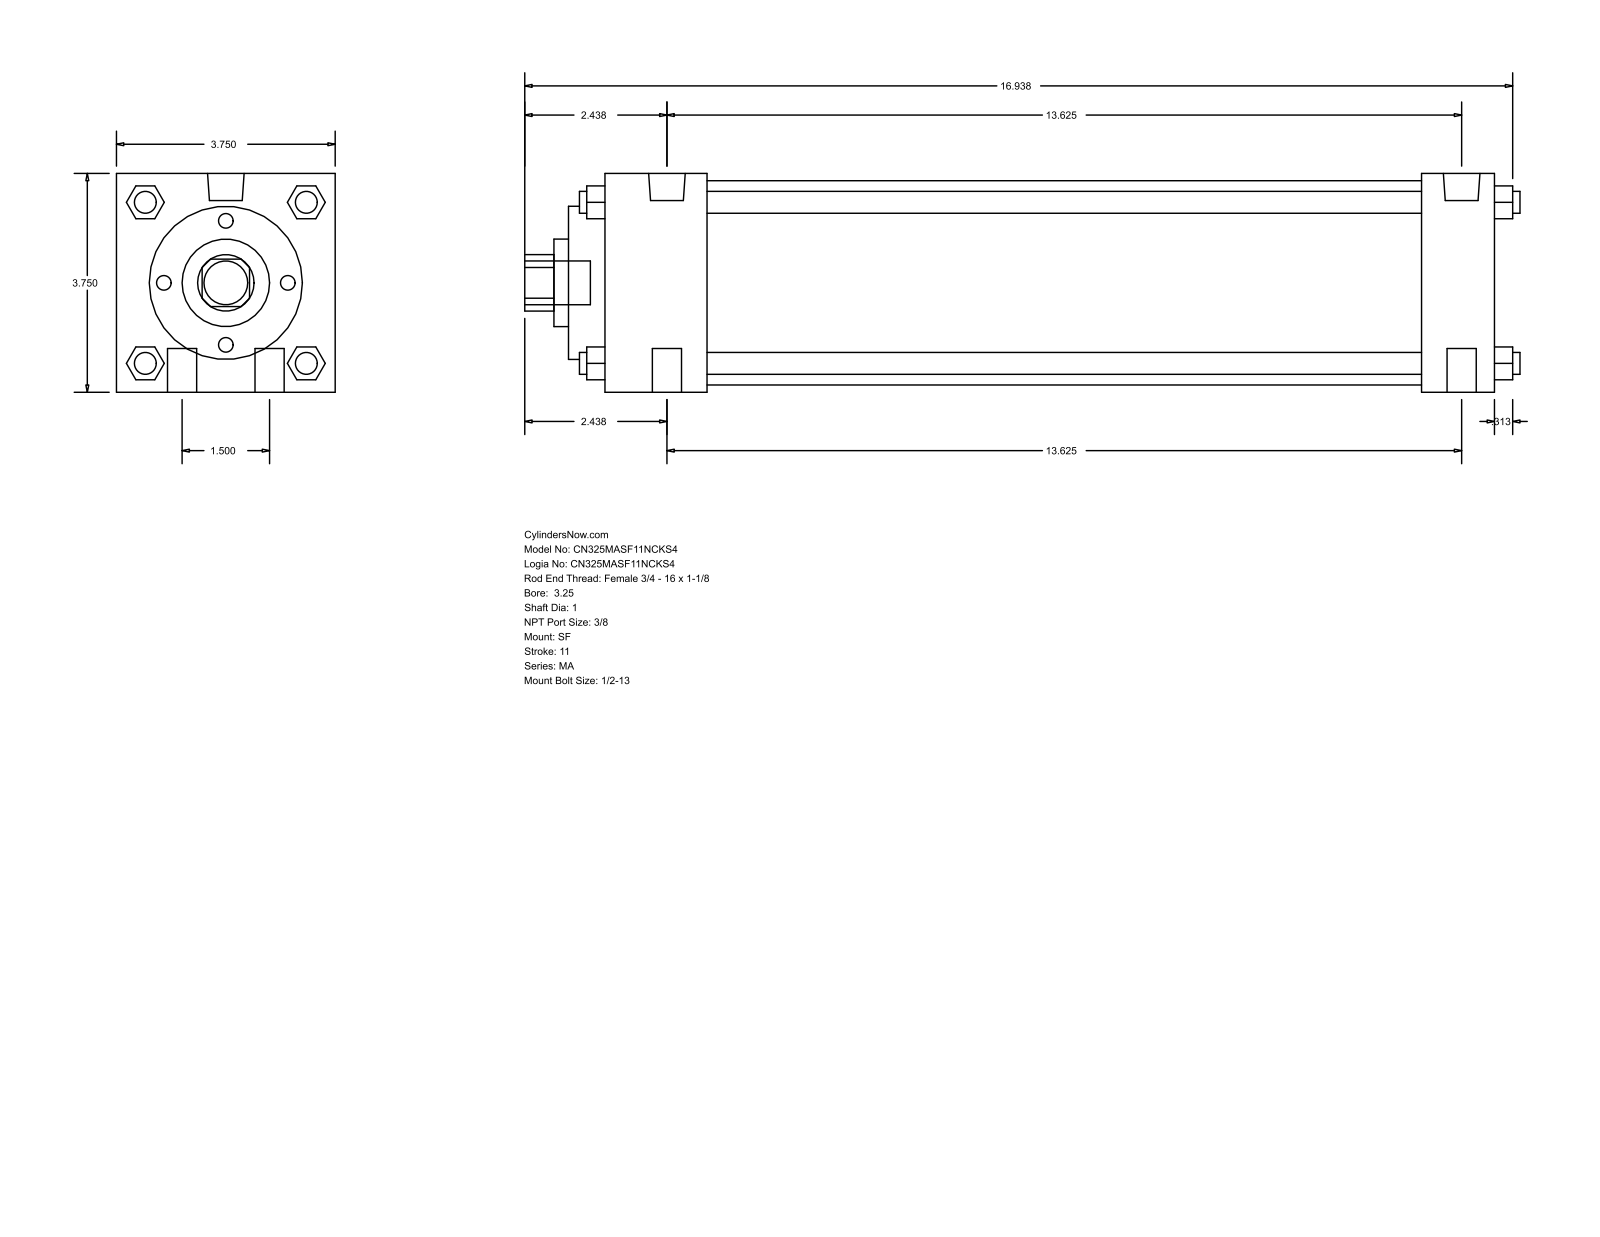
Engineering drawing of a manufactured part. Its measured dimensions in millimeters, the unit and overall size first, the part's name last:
Units: millimetres
Overall size (bounding box): 433.39 × 95.25 × 95.25
Round holes (diameter × count): ⌀25.4 ×1, ⌀38.1 ×1, ⌀66.67 ×1, ⌀88.9 ×1
Round bosses / shafts (diameter × count): ⌀12.7 ×4, ⌀9.53 ×4, ⌀15.93 ×2, ⌀11.11 ×2, ⌀19.05 ×1
Partial cylindrical surfaces — rounded edges, fillets, slot ends (radius × count): R12.29 ×1
Main face-to-face distances: 95.24, 387.35, 403.22, 15.87, 355.6, 31.75, 44.46, 311.14, 342.89, 60.33
Bodies: 0 solids, 126 faces (95 planar, 31 cylindrical, 0 other)
Part name (STEP PRODUCT): MA_SF__0325_1
STEP written by: GSSL Pune (CONFIG_CONTROL_DESIGN)
